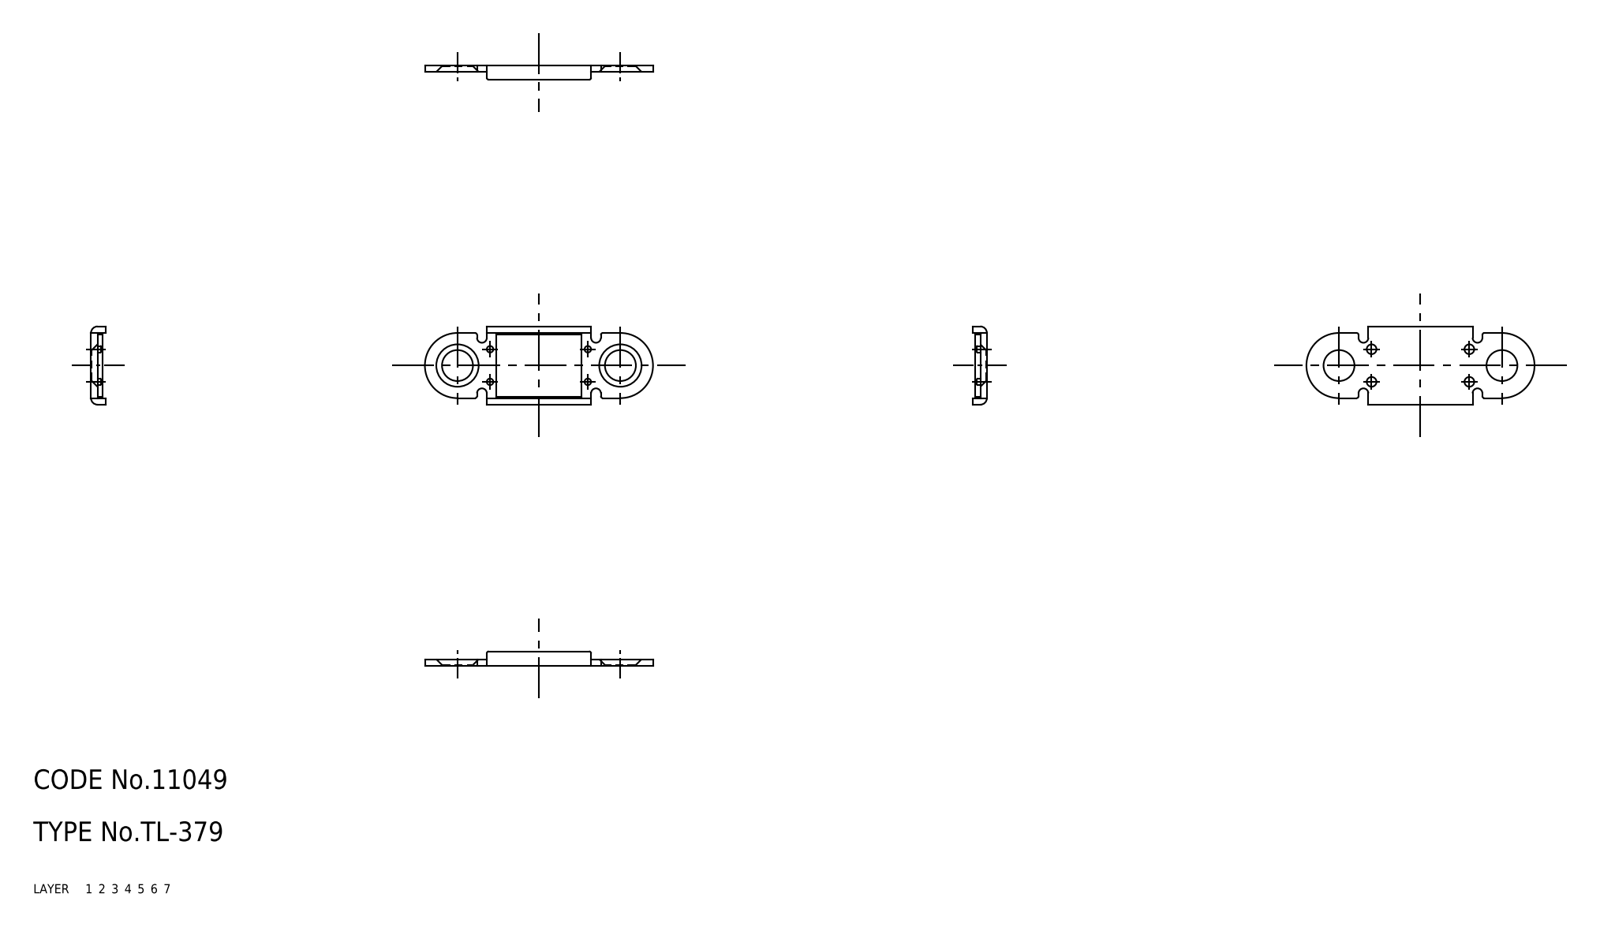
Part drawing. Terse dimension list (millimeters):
name: 67113586
written by: CADfix (AUTOMOTIVE_DESIGN)
unit: mm
bodies: 1 solid, 81 faces (0 planar, 0 cylindrical, 81 other)
size: 35 × 12 × 2.2
volume: 432 mm³; area: 862 mm²
